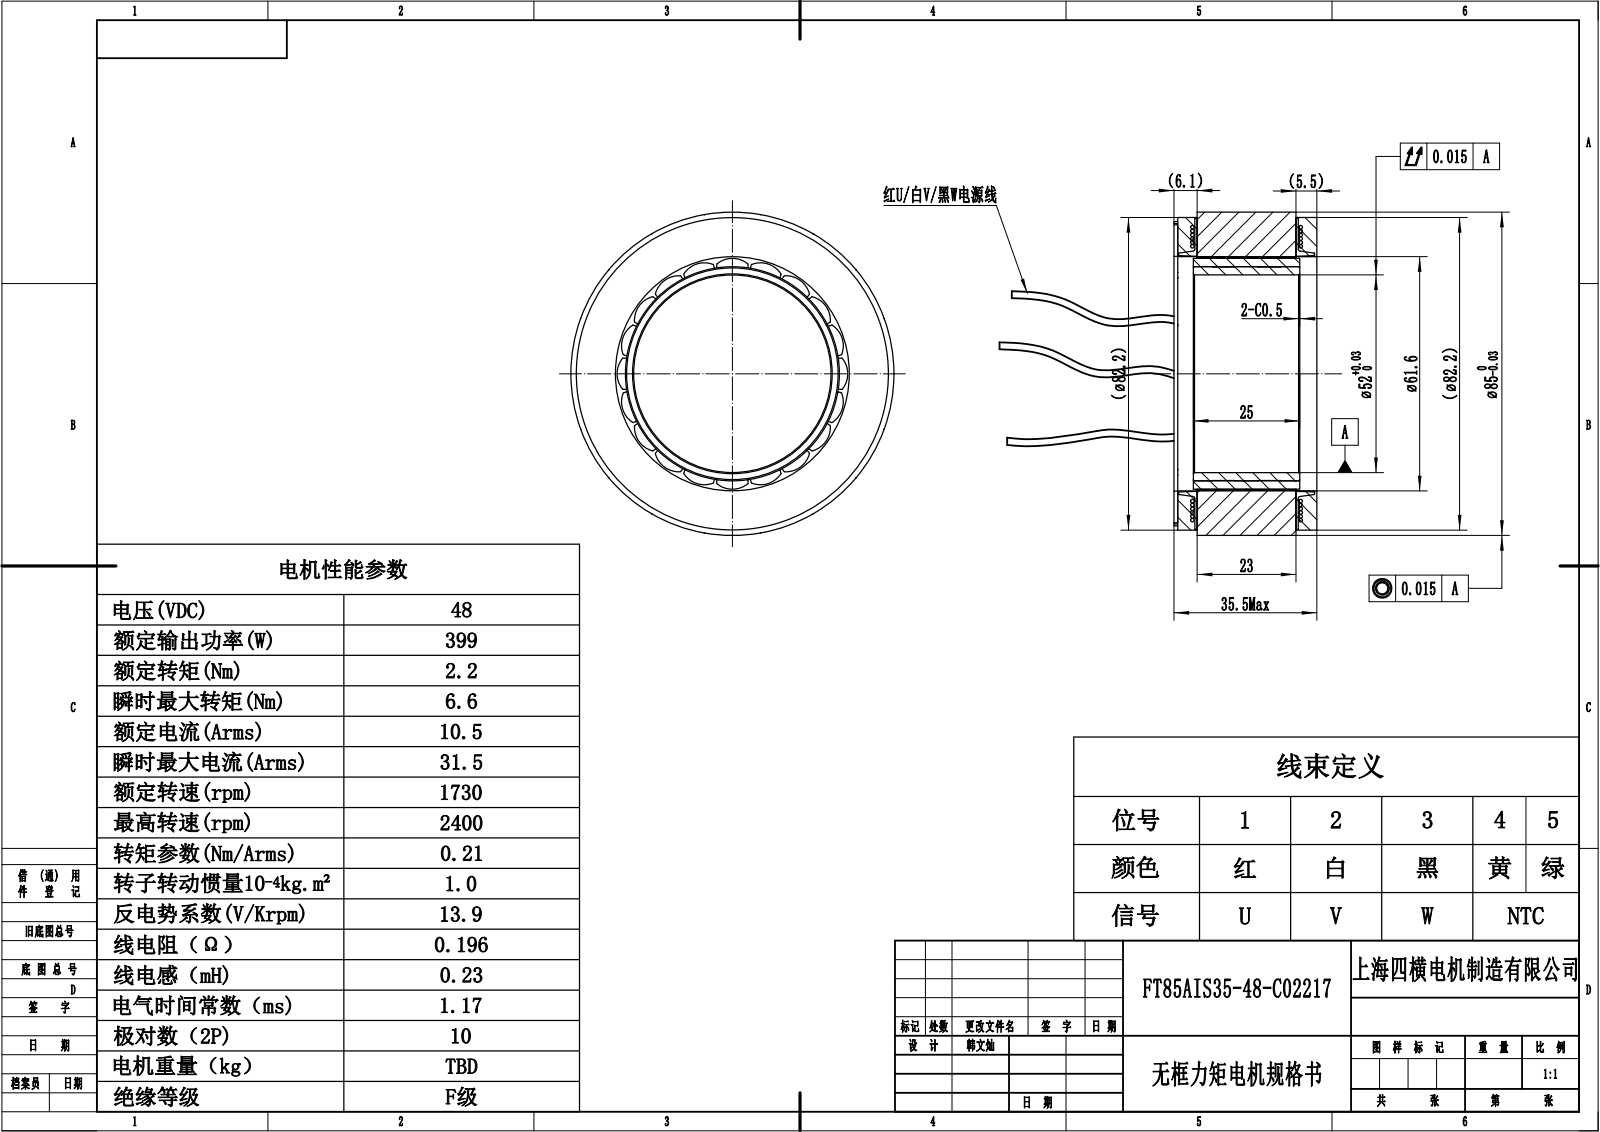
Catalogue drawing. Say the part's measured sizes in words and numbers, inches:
The part is named "85骨架H11.5; 85灌胶H5.5; 85转子铁芯H25+磁钢; 85定子铁芯H23 (+6 more)". Its 3-D file was written by "SolidWorks 2024 (CONFIG_CONTROL_DESIGN)". It is 169 solids with 7424 faces: 1738 planar, 2978 cylindrical and 2708 other. Overall it measures 3.346 by 3.346 by 1.362 inches. Its volume is 5.429 cubic inches and its surface area 185 square inches. Round holes: 3 of diameter 0.079, 1 of diameter 2.047, 1 of diameter 2.217, 1 of diameter 2.425, 1 of diameter 2.429. Round bosses or shafts: 432 of diameter 0.039, 1 of diameter 3.346, 1 of diameter 3.236, 1 of diameter 3.142, 1 of diameter 2.209. Partial cylindrical surfaces (rounded edges, fillets, slot ends): 396 of radius 0.006, 388 of radius 0.02, 180 of radius 0.008, 172 of radius 0.014, 96 of radius 0.039, 60 of radius 0.079, 36 of radius 0.004, 36 of radius 0.022. The main face-to-face distances are 0.201, 0.906, 1.106, 0.14, 0.15, 1.35, 0.039, 1.146, 1.201, 1.35. The hole center spacings are 1.496, 0.774, 1.496.
